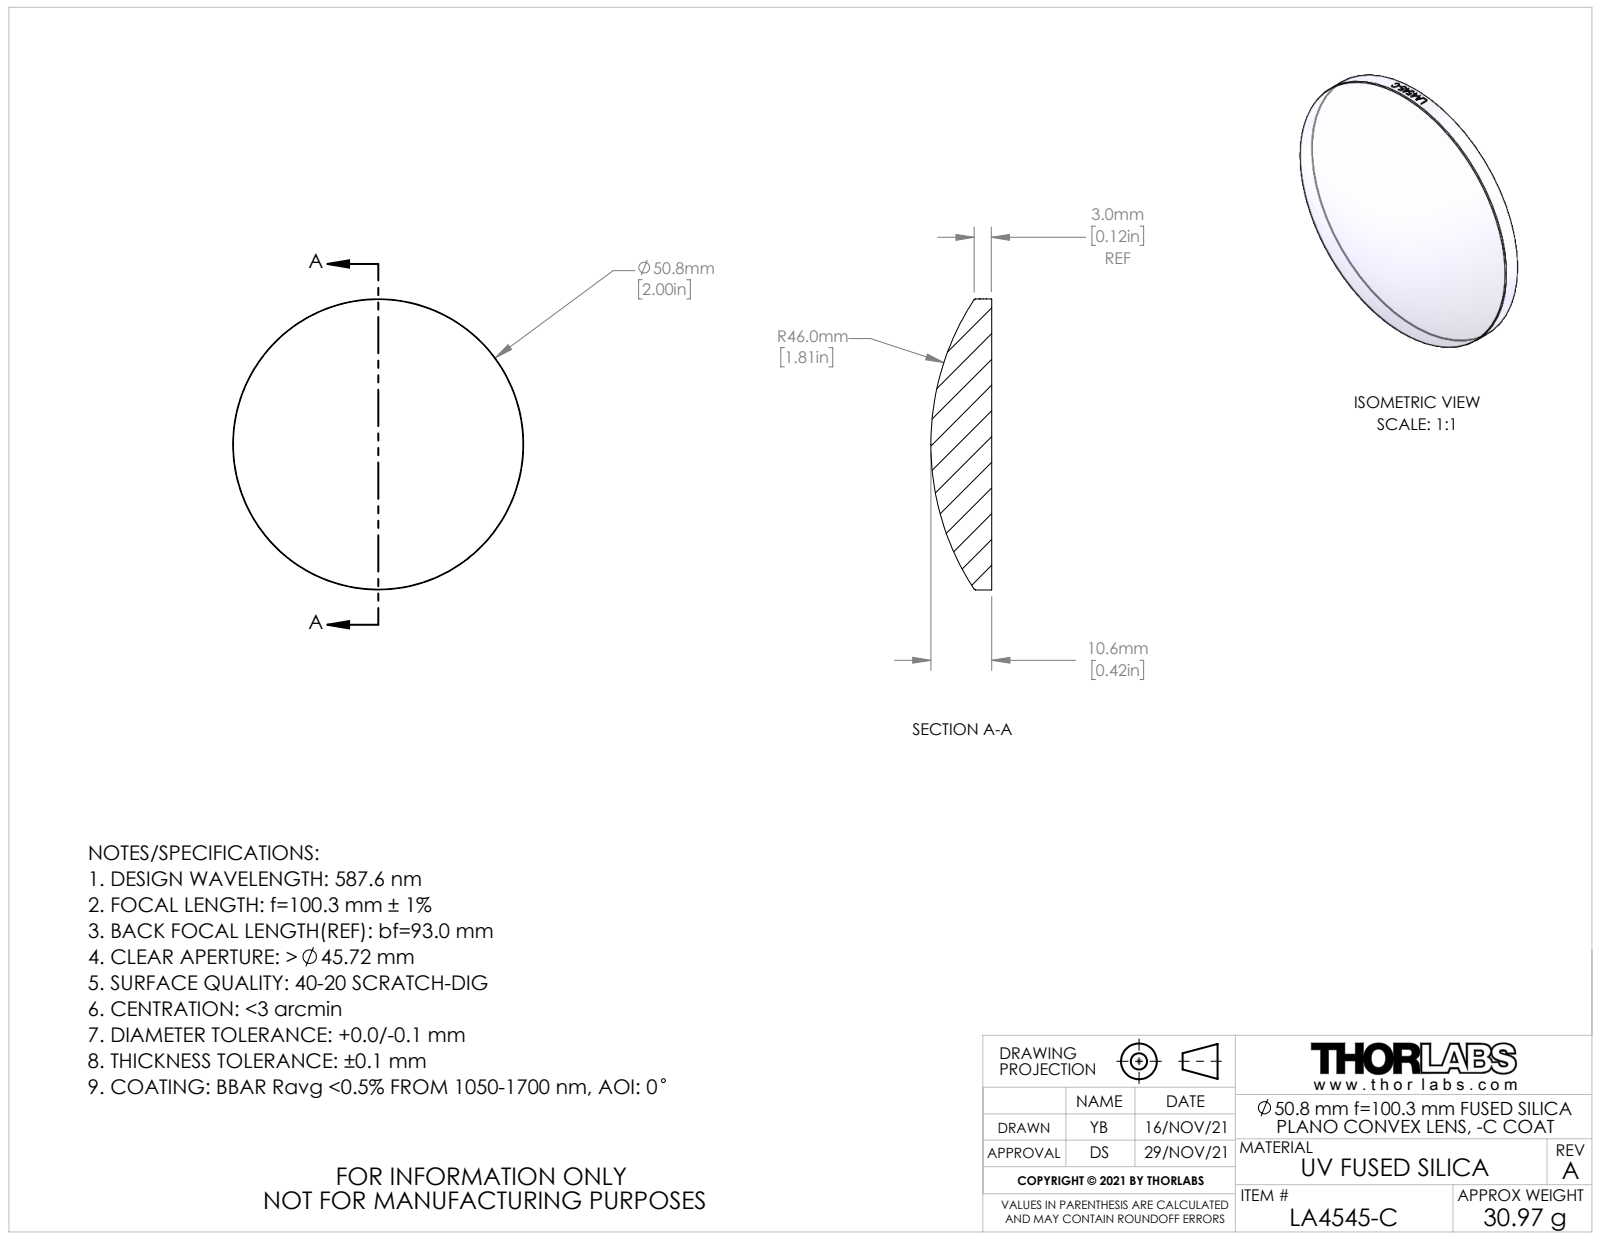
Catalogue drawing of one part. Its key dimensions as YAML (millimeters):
part_name: "CTN018143; CTN018074-E0W"
step_written_by: "SolidWorks 2018 (AUTOMOTIVE_DESIGN)"
units: millimeters
bodies: {solids: 1, faces: 20, planar: 1, cylindrical: 13, other: 6}
overall_size: [50.8, 50.8, 10.64]
volume: 14057
surface_area: 4701
round_bosses_or_shafts:
  - {diameter: 50.8, count: 1}
